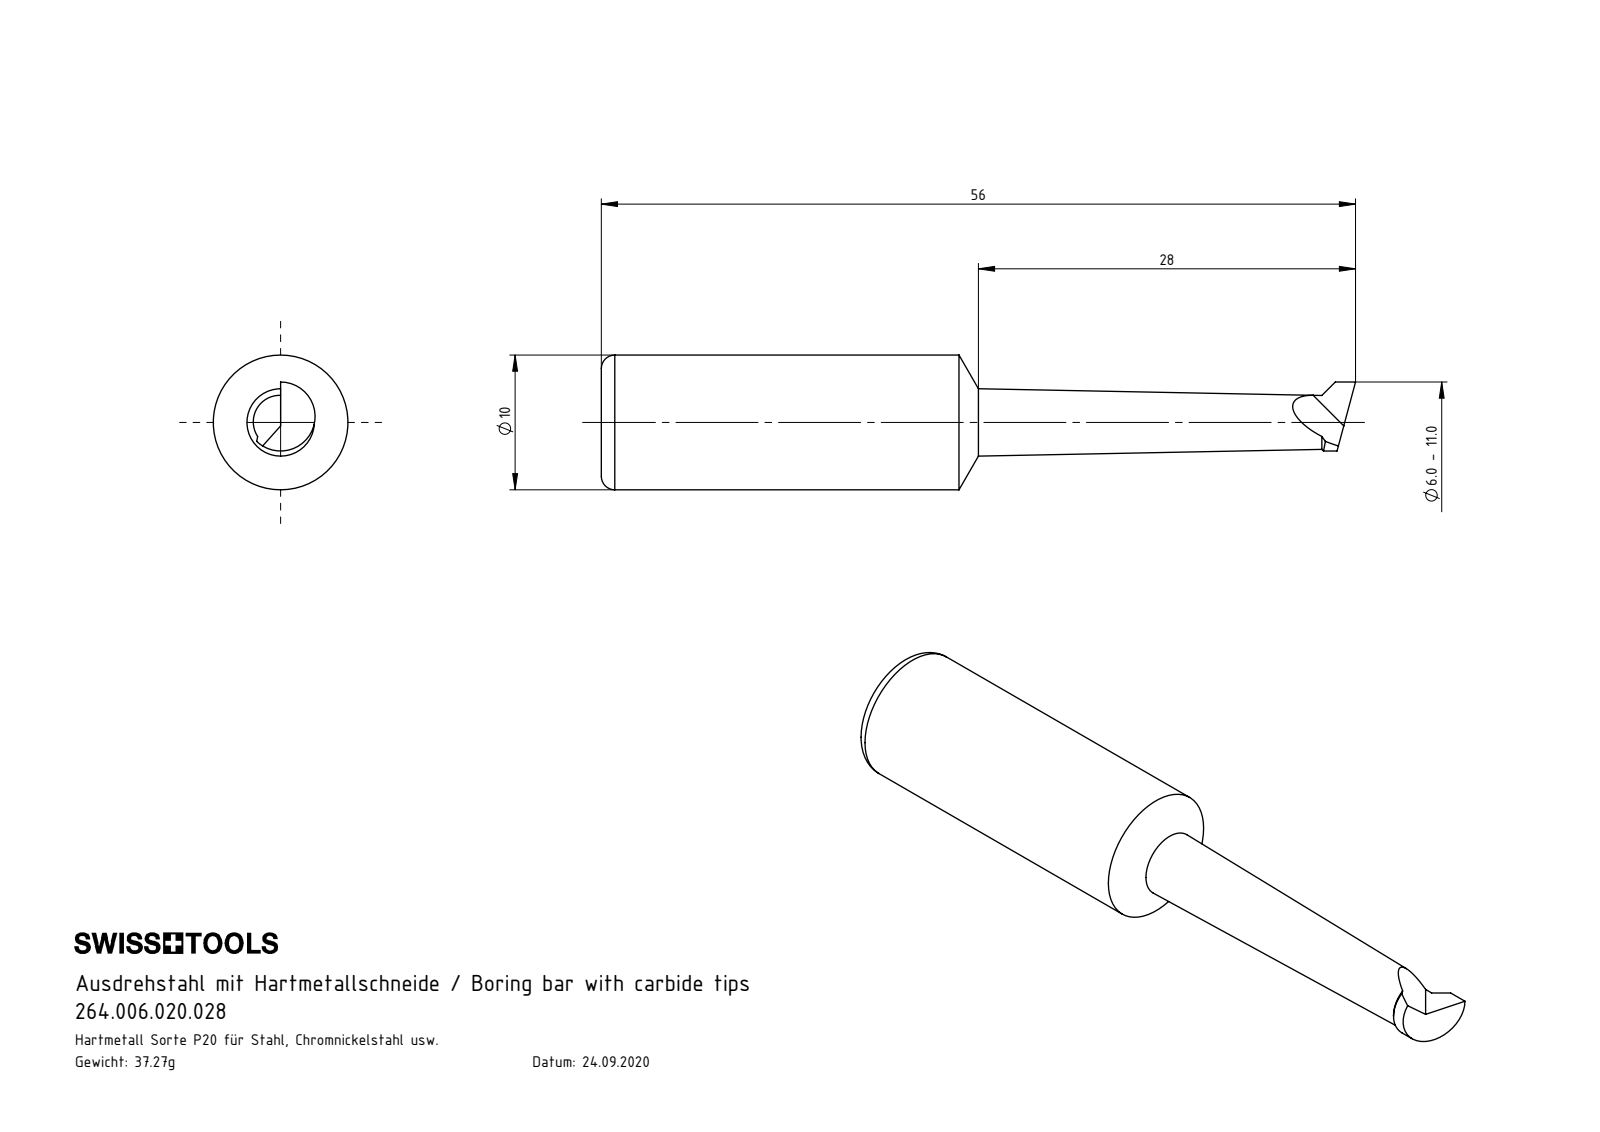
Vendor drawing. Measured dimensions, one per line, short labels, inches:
name: U10.B06.002.028
written by: SolidWorks 2017 (AUTOMOTIVE_DESIGN)
unit: in
bodies: 1 solid, 10 faces (4 planar, 2 cylindrical, 4 other)
size: 2.205 × 0.394 × 0.394
volume: 0.157 in³; area: 2.119 in²
bosses: 1× ⌀0.394
rounds: 1× R0.101
